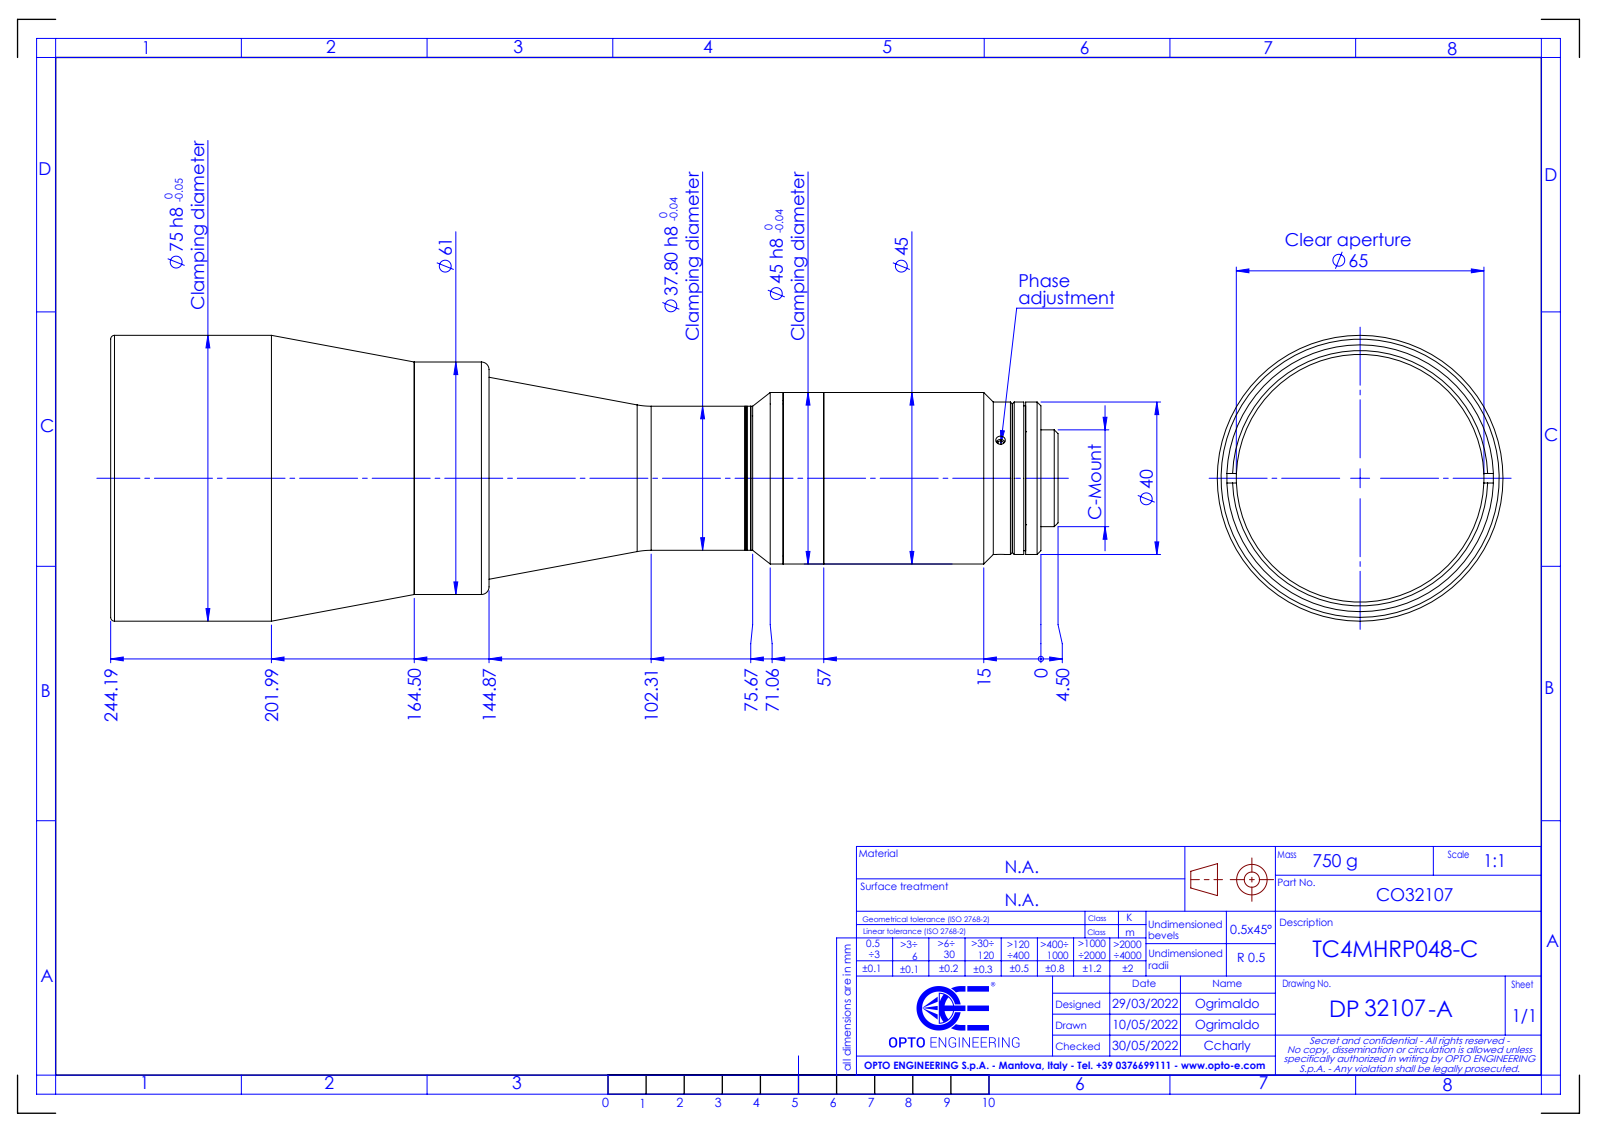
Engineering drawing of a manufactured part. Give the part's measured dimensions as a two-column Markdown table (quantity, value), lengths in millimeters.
| quantity | value |
| --- | --- |
| part name | DP32107-A_TC4MHRP048-C |
| STEP written by | SolidWorks 2021 (CONFIG_CONTROL_DESIGN) |
| units | millimeters |
| bodies | 0 solids, 87 faces (19 planar, 42 cylindrical, 26 other) |
| overall size | 248.69 × 75 × 75 |
| round holes (diameter × count) | 2.5 × 3, 22.5 × 1, 53 × 1, 65 × 1, 70 × 1 |
| round bosses / shafts (diameter × count) | 75 × 1, 61 × 1, 45 × 1, 40 × 1, 37.8 × 1, 25.4 × 1 |
| main face-to-face distances | 0.5, 4.5, 4, 160, 160.5, 164.5, 79.38, 239.38, 239.88, 243.88 |
